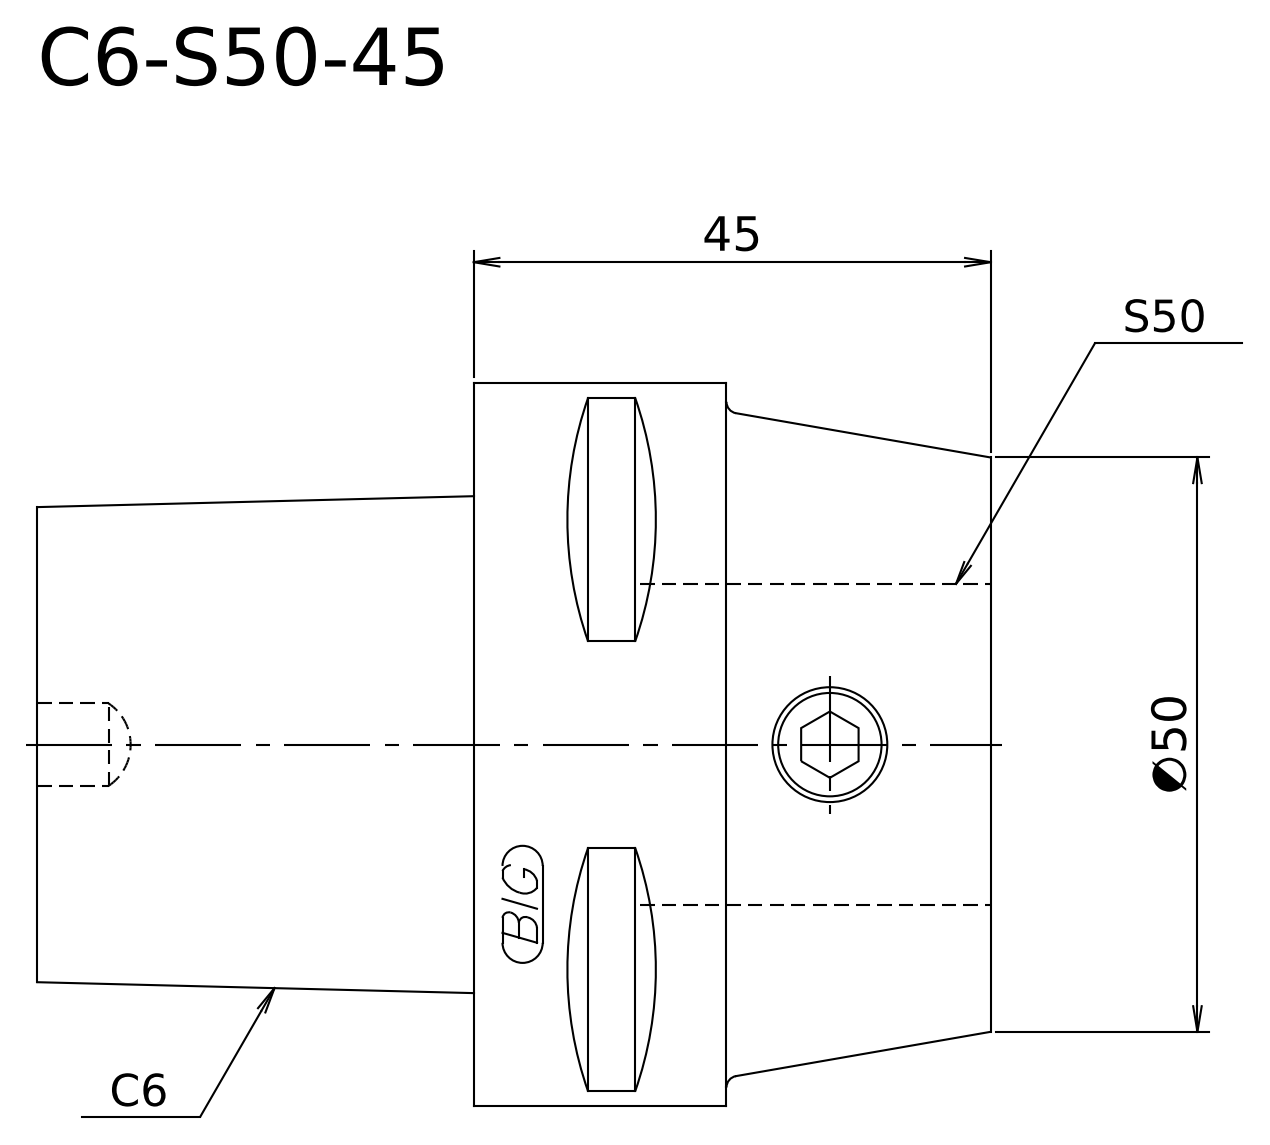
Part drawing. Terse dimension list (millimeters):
name: C6-S50-45
written by: SolidWorks 2021 (CONFIG_CONTROL_DESIGN)
unit: mm
bodies: 1 solid, 12 faces (4 planar, 2 cylindrical, 6 other)
size: 83 × 63 × 63
volume: 174 816 mm³; area: 18 746 mm²
bosses: 1× ⌀63
face distances: 45, 38, 83, 60, 22, 23
